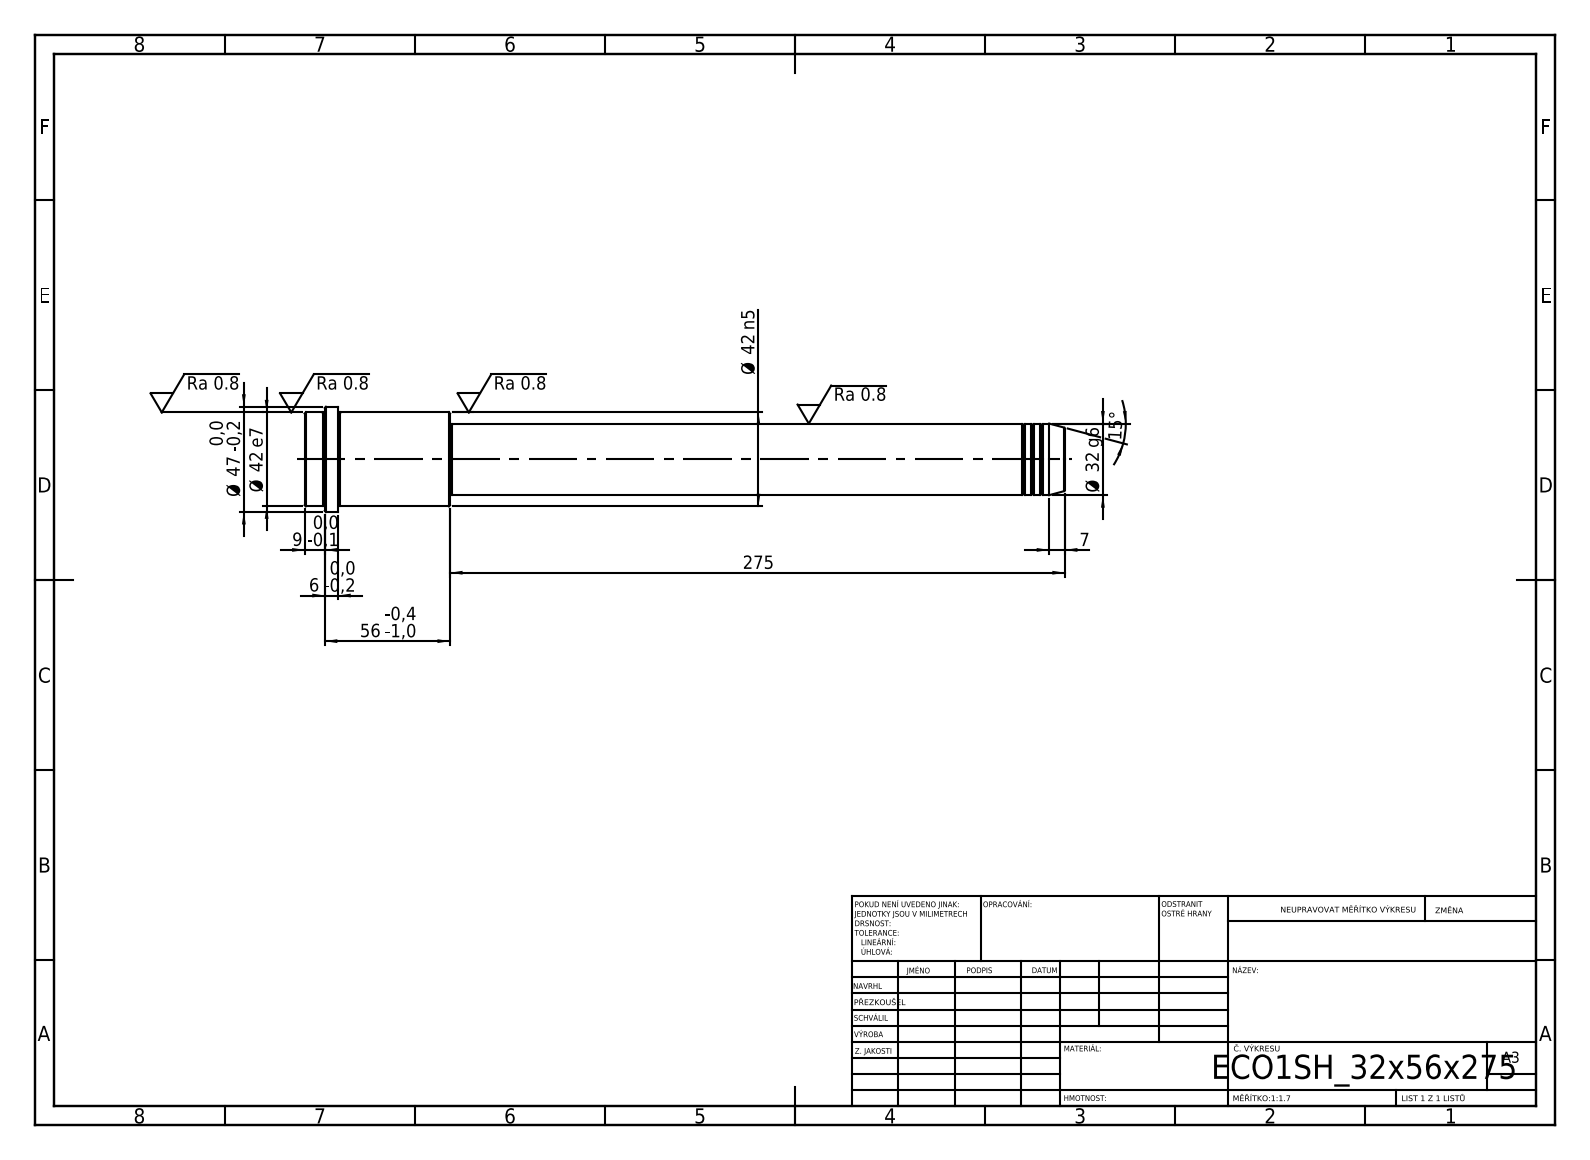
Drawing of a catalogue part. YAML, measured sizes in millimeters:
step_written_by: "SolidWorks 2019 (CONFIG_CONTROL_DESIGN)"
units: millimeters
bodies: {solids: 1, faces: 52, planar: 6, cylindrical: 16, other: 30}
overall_size: [340, 47, 47]
volume: 312362
surface_area: 39863
round_bosses_or_shafts:
  - {diameter: 47, count: 1}
  - {diameter: 42, count: 1}
  - {diameter: 32, count: 1}
  - {diameter: 31, count: 1}
face_to_face_distances: [340, 275, 65, 325, 50, 15, 331, 56, 6, 9]
